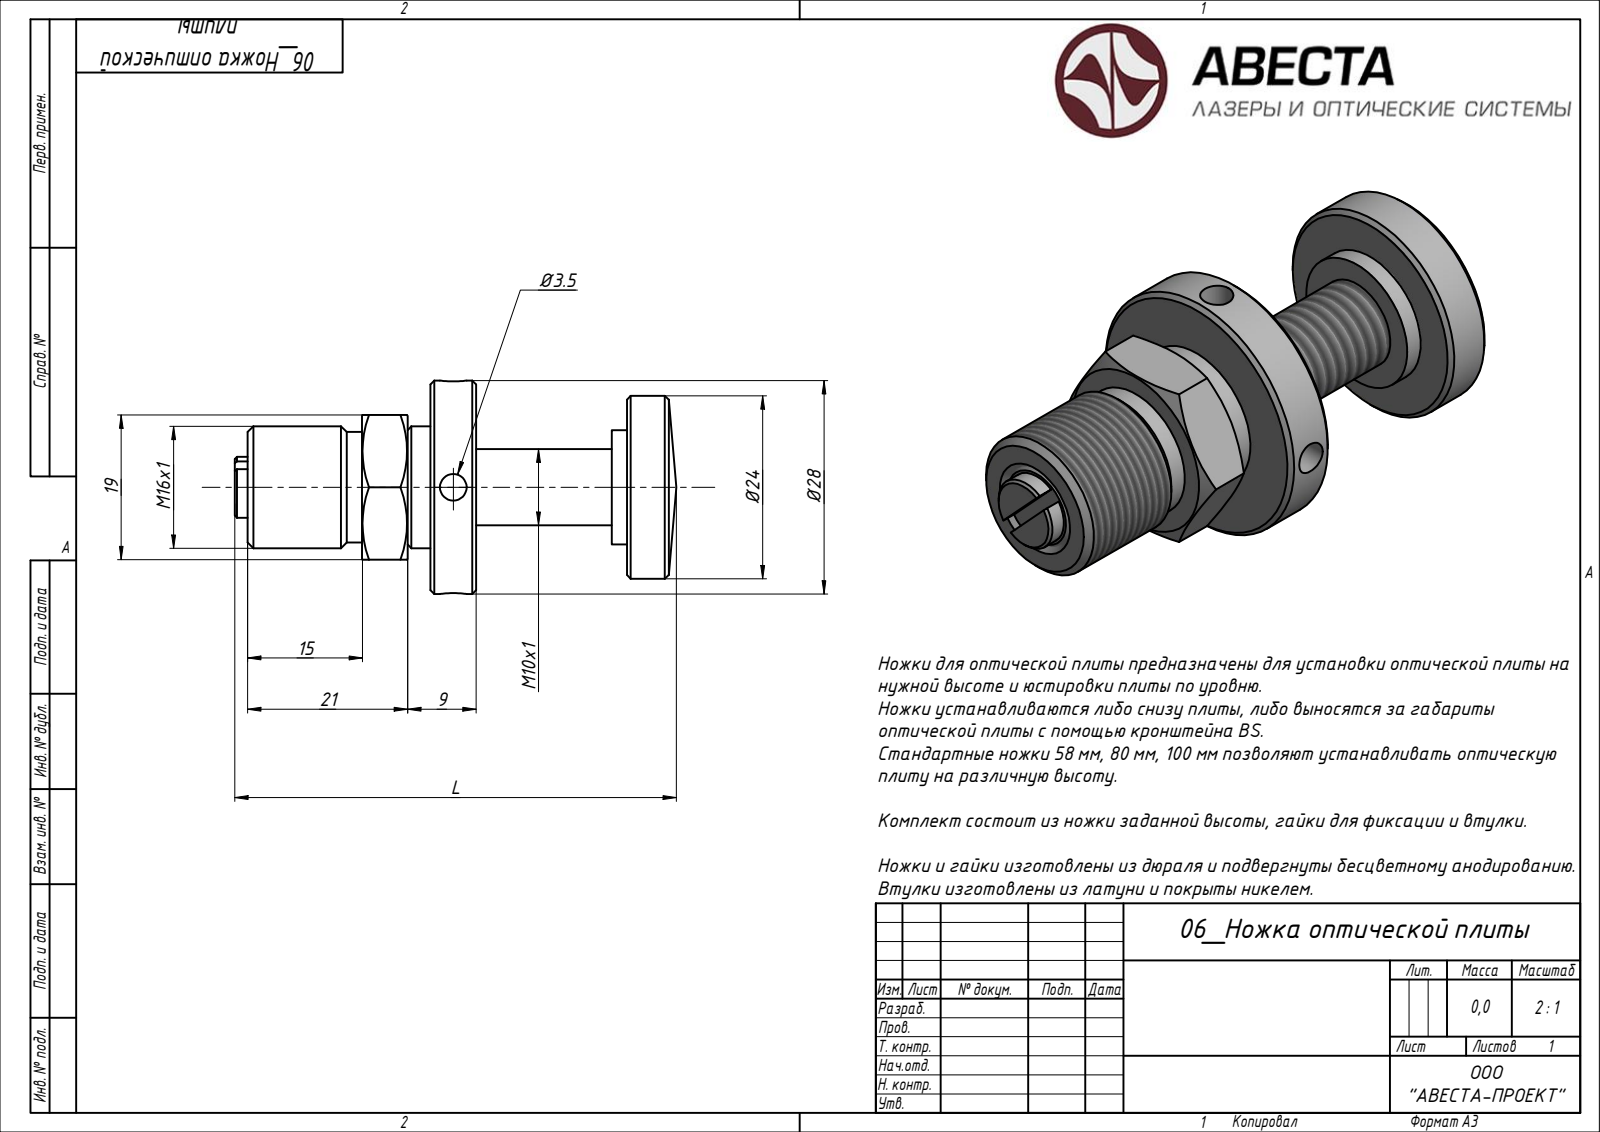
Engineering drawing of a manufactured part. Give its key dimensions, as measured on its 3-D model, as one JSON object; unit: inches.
{"part_name": "06_Ножка оптической плиты; 03_Ножка; 02_Контргайка; 01_Гайка", "step_written_by": "Autodesk Inventor 2020 (AUTOMOTIVE_DESIGN)", "units": "inches", "bodies": {"solids": 3, "faces": 54, "planar": 19, "cylindrical": 15, "other": 20}, "overall_size": [2.283, 1.102, 1.102], "volume_in3": 0.834, "surface_area_in2": 11.38, "round_holes": [[0.138, 2], [0.351, 1], [0.351, 1]], "round_bosses_or_shafts": [[1.102, 1], [0.945, 1], [0.63, 1], [0.591, 1], [0.571, 1], [0.394, 1], [0.315, 1]], "face_to_face_distances": [0.236, 0.354, 0.118, 1.134, 1.016, 0.78, 0.591, 0.748, 0.079, 1.37]}
